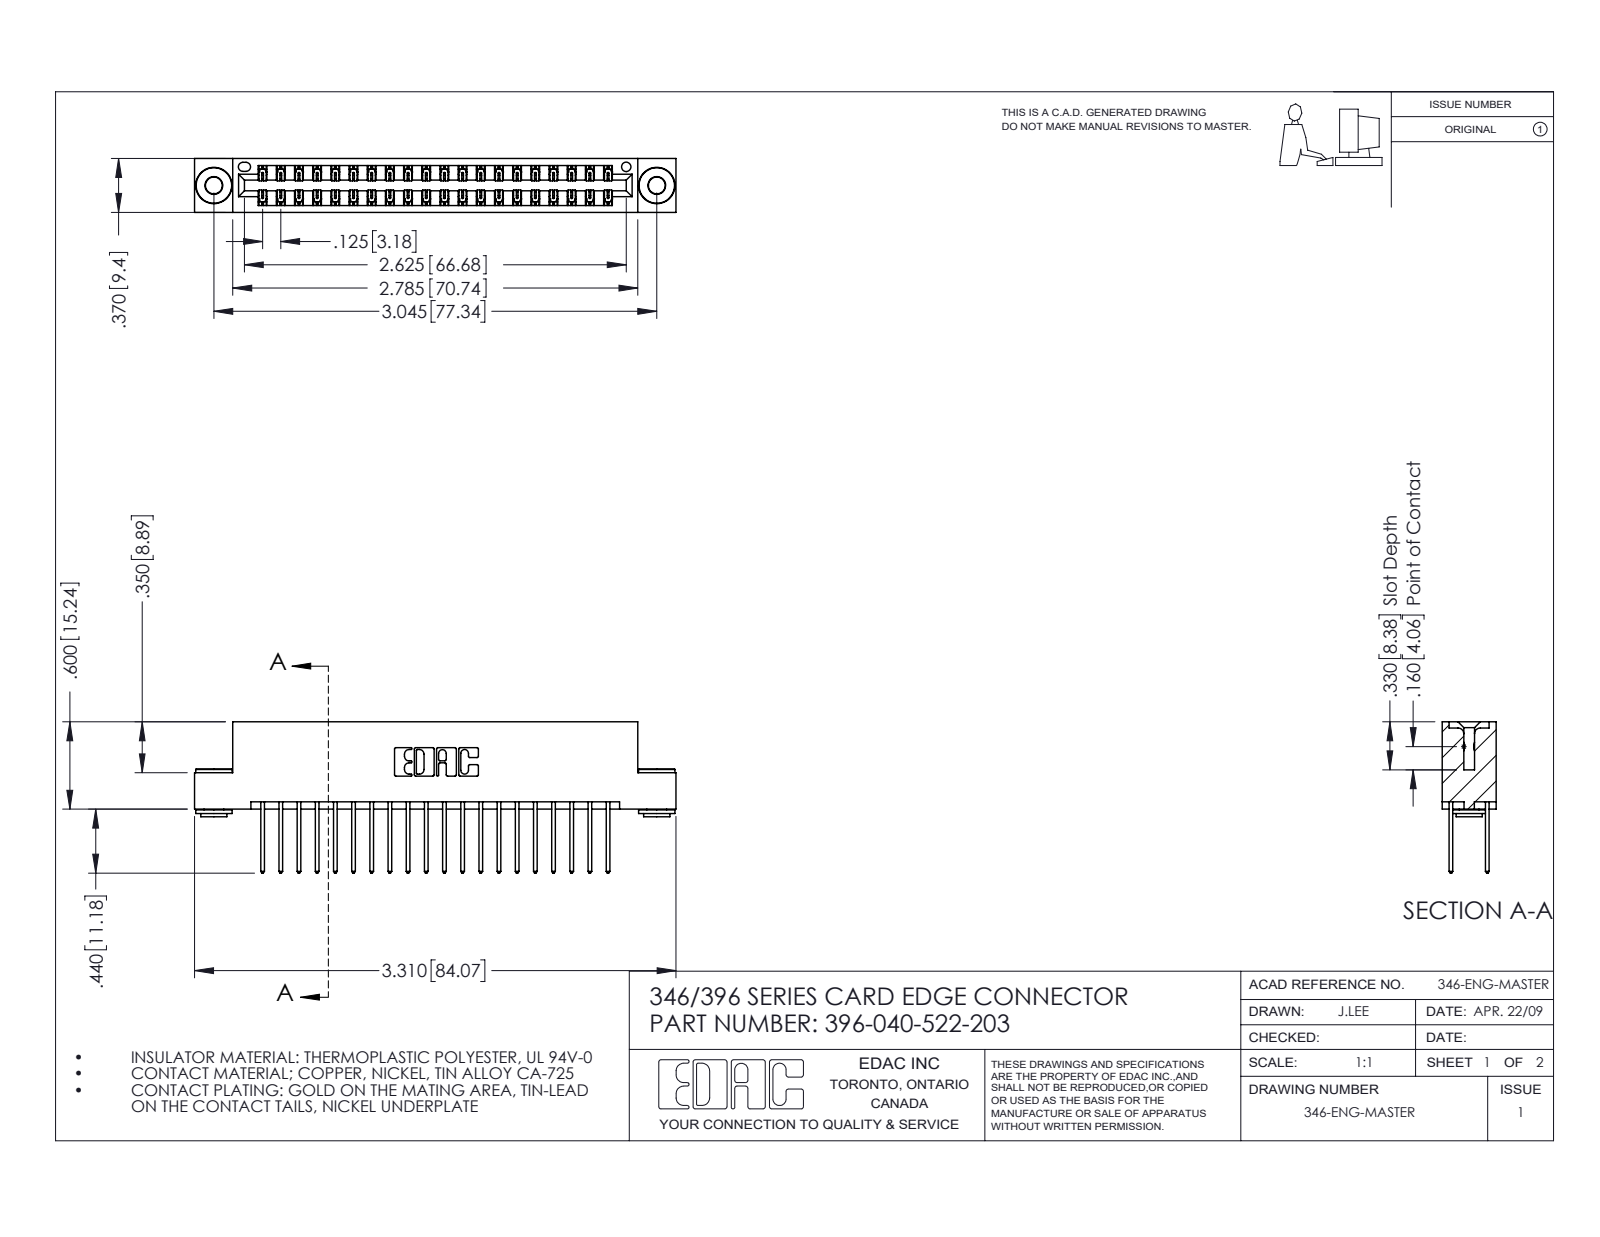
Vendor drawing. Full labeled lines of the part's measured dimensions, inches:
Part name (STEP PRODUCT): 396-040-522-203; 345-250-002_345-250-002-102; 345-292-001_345-293-122; 346 Part_Flush Mounting Lugs - 0.156 Dia-TH
STEP written by: SolidWorks 2016 (CONFIG_CONTROL_DESIGN)
Units: inches
Bodies: 43 solids, 2240 faces (1486 planar, 746 cylindrical, 8 other)
Overall size (bounding box): 3.31 × 1.04 × 0.37
Volume: 0.497 in³ · Surface area: 17.9 in²
Round holes (diameter × count): ⌀0.116 ×2, ⌀0.156 ×2, ⌀0.064 ×1
Round bosses / shafts (diameter × count): ⌀0.25 ×2, ⌀0.18 ×2, ⌀0.136 ×2
Partial cylindrical surfaces — rounded edges, fillets, slot ends (radius × count): R0.006 ×60, R0.01 ×40, R0.01 ×22, R0.007 ×6, R0.031 ×6, R0.026 ×3, R0.014 ×2, R0.022 ×2
Main face-to-face distances: 0.048, 0.322, 0.25, 0.37, 0.025, 0.072, 0.298, 0.275, 0.148, 0.222
Hole centre spacings: 0.246, 2.837, 3.045
